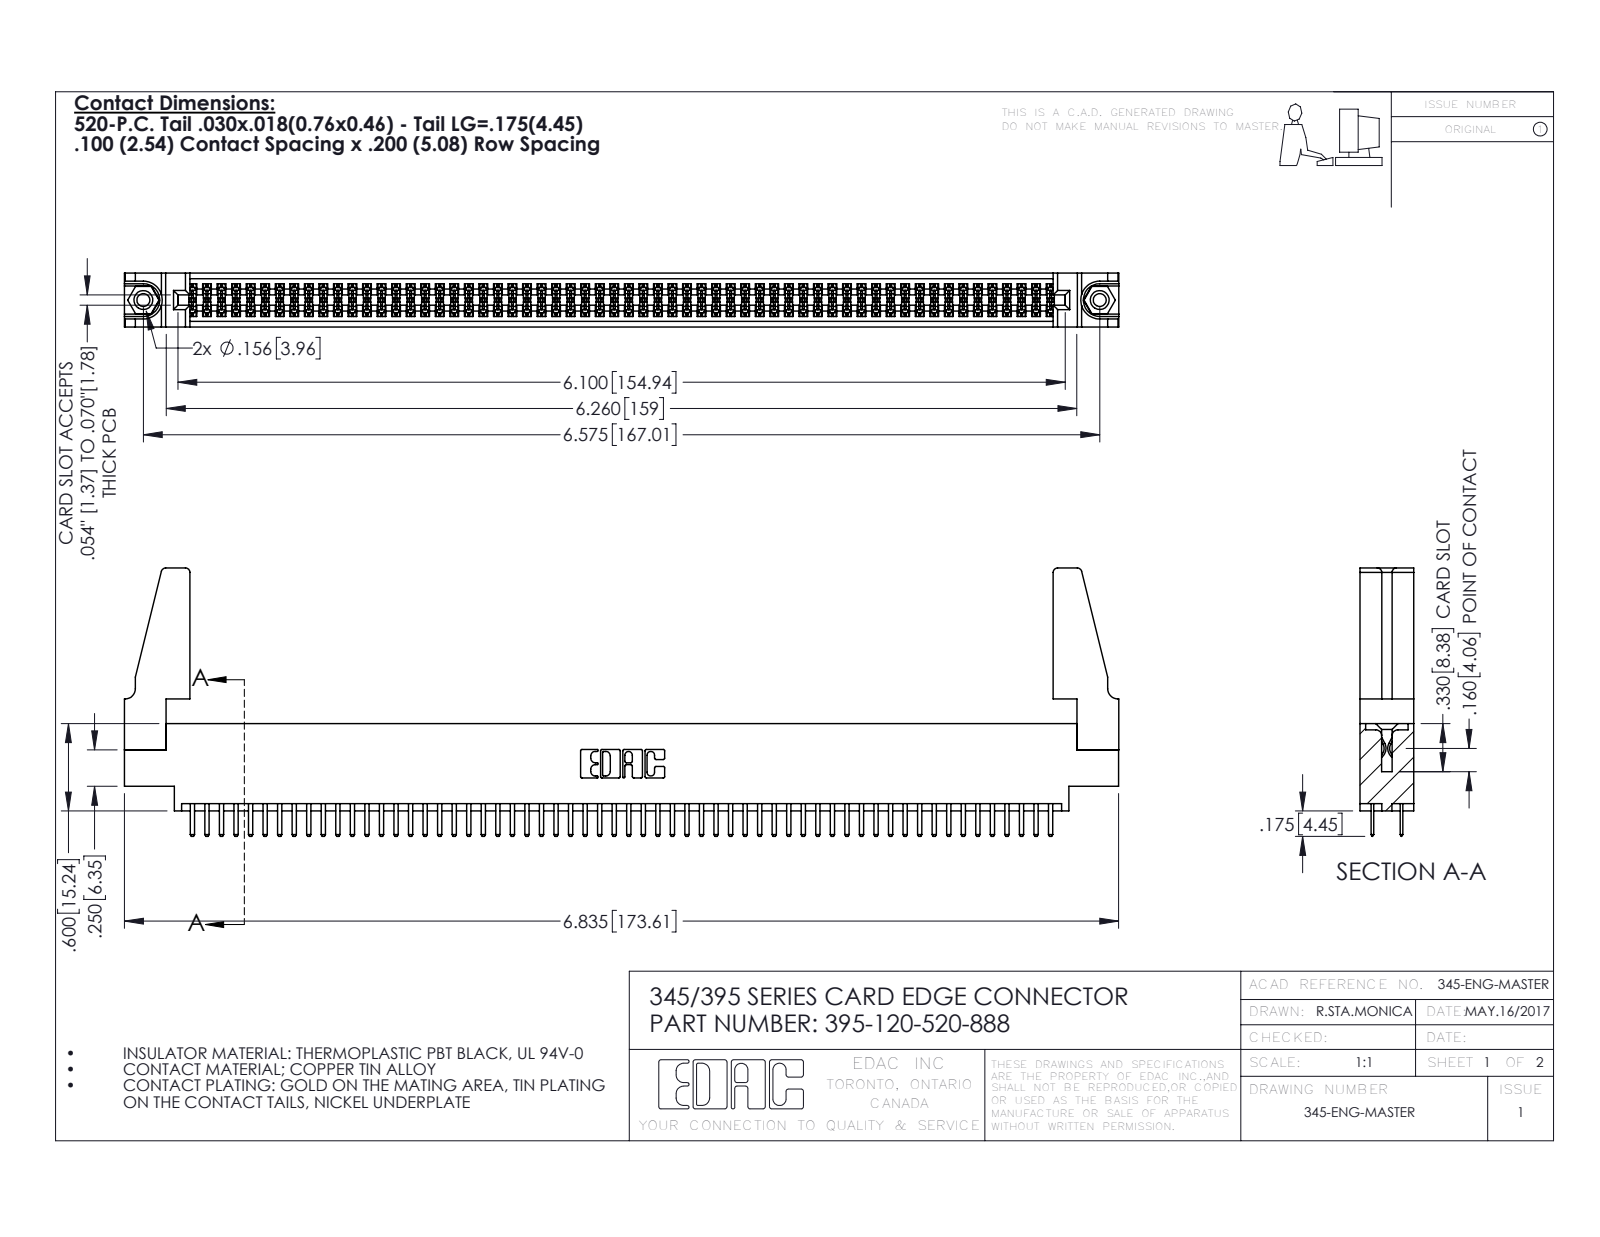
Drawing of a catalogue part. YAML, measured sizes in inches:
part_name: "345-292-001_345-293-120; 345 Part_0.170 Offset - 0.156 Dia-TH; 345-250-001_345-250-001-102; 345-220-078_345-220-088 (+1 more)"
step_written_by: "SolidWorks 2016 (CONFIG_CONTROL_DESIGN)"
units: inches
bodies: {solids: 125, faces: 6734, planar: 4356, cylindrical: 2362, other: 16}
overall_size: [6.836, 1.845, 0.37]
volume: 1.228
surface_area: 44.08
round_holes:
  - {diameter: 0.089, count: 2}
  - {diameter: 0.125, count: 2}
  - {diameter: 0.156, count: 2}
  - {diameter: 0.064, count: 1}
round_bosses_or_shafts:
  - {diameter: 0.155, count: 2}
partial_cylinders:
  - {radius: 0.006, count: 180}
  - {radius: 0.01, count: 124}
  - {radius: 0.01, count: 22}
  - {radius: 0.03, count: 8}
  - {radius: 0.007, count: 6}
  - {radius: 0.031, count: 6}
  - {radius: 0.026, count: 3}
  - {radius: 0.014, count: 2}
face_to_face_distances: [0.072, 0.298, 0.37, 0.2, 0.098, 0.272, 0.025, 0.225, 0.022, 0.072]
hole_center_spacings: [0.27, 6.339, 6.575]
